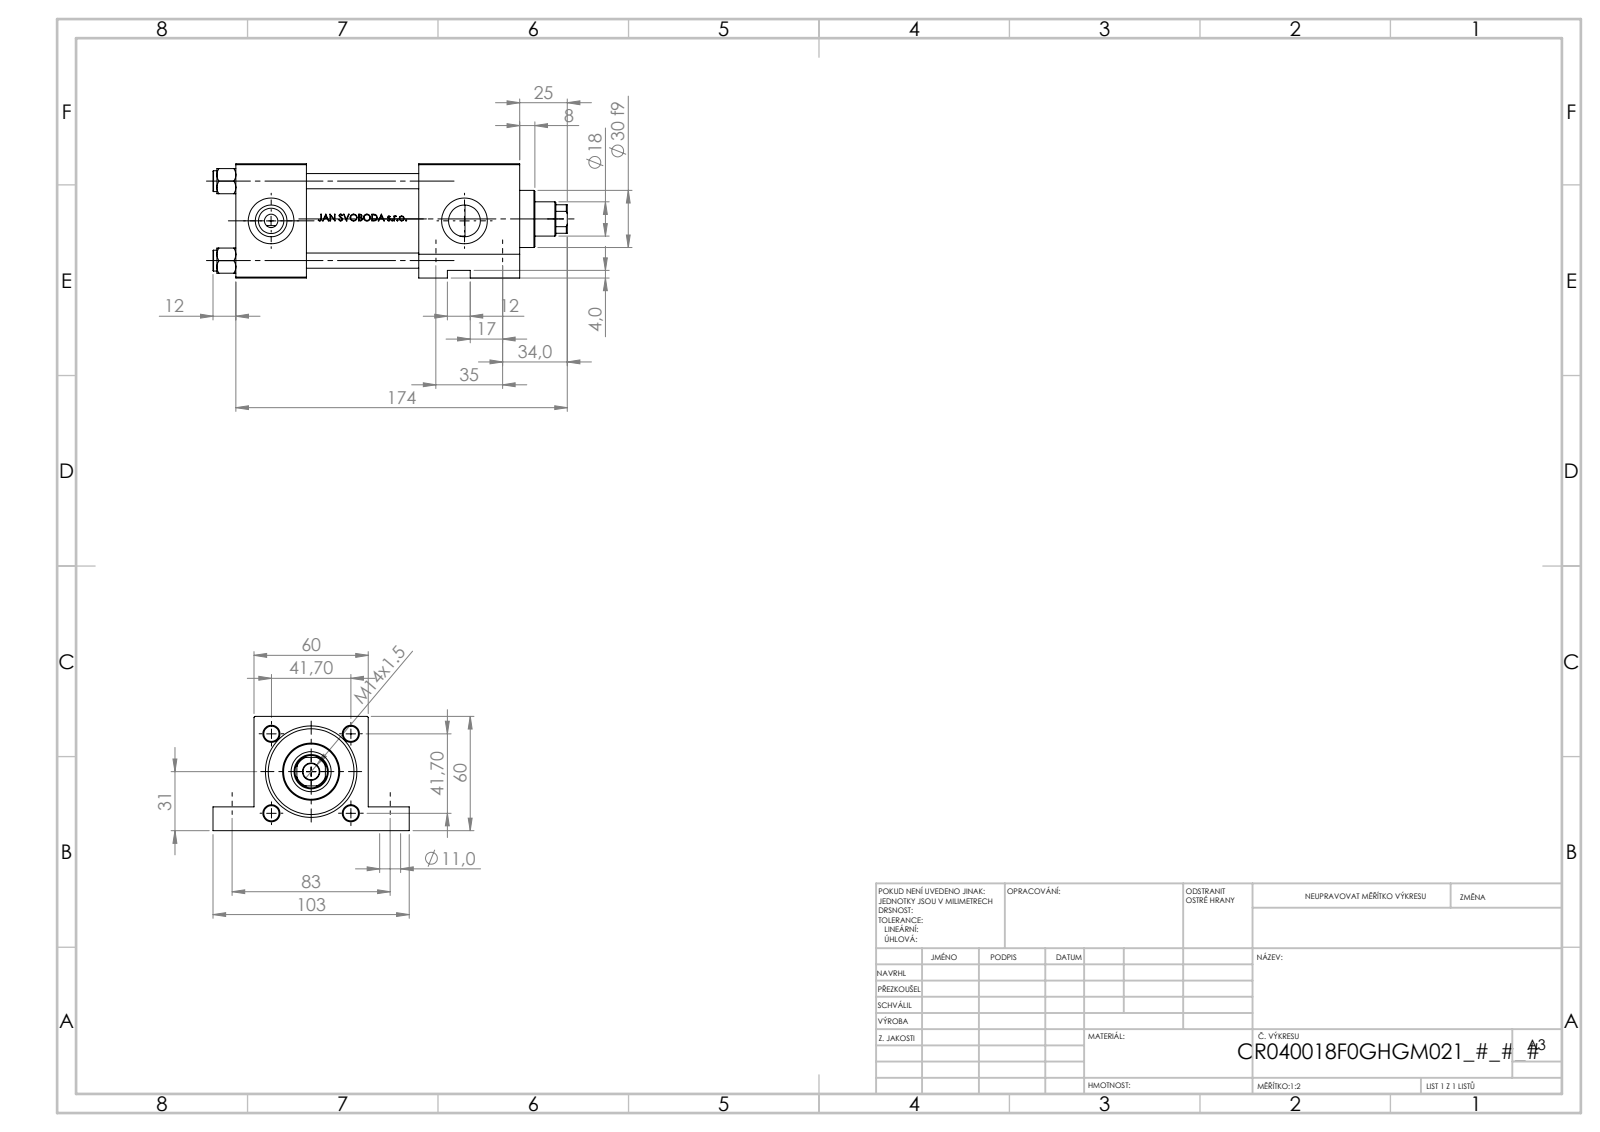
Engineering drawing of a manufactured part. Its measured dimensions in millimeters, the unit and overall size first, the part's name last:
Units: millimetres
Overall size (bounding box): 186 × 103 × 60
Round holes (diameter × count): ⌀8 ×4, ⌀7 ×2, ⌀11 ×2, ⌀11 ×2, ⌀16.66 ×2, ⌀24 ×2, ⌀8.5 ×1, ⌀18 ×1, ⌀21 ×1, ⌀31 ×1, ⌀40 ×1, ⌀45 ×1
Round bosses / shafts (diameter × count): ⌀11 ×4, ⌀46 ×1, ⌀30 ×1
Partial cylindrical surfaces — rounded edges, fillets, slot ends (radius × count): R8.5 ×1
Main face-to-face distances: 60, 37, 149, 112, 59, 96, 53, 120.3, 83.3, 24.3
Hole centre spacings: 41.7, 28.79, 30.2, 35, 58.97, 83, 90.08, 101.5
Volume: 424 492 mm³ · Surface area: 111 964 mm²
Bodies: 11 solids, 1118 faces (437 planar, 141 cylindrical, 540 other)
Part name (STEP PRODUCT): NUT_M5_F; V215CR_VCP_F; V215CR_F_TYCINKA; V215_VC_A (+1 more)
STEP written by: SolidWorks 2019 (CONFIG_CONTROL_DESIGN)
